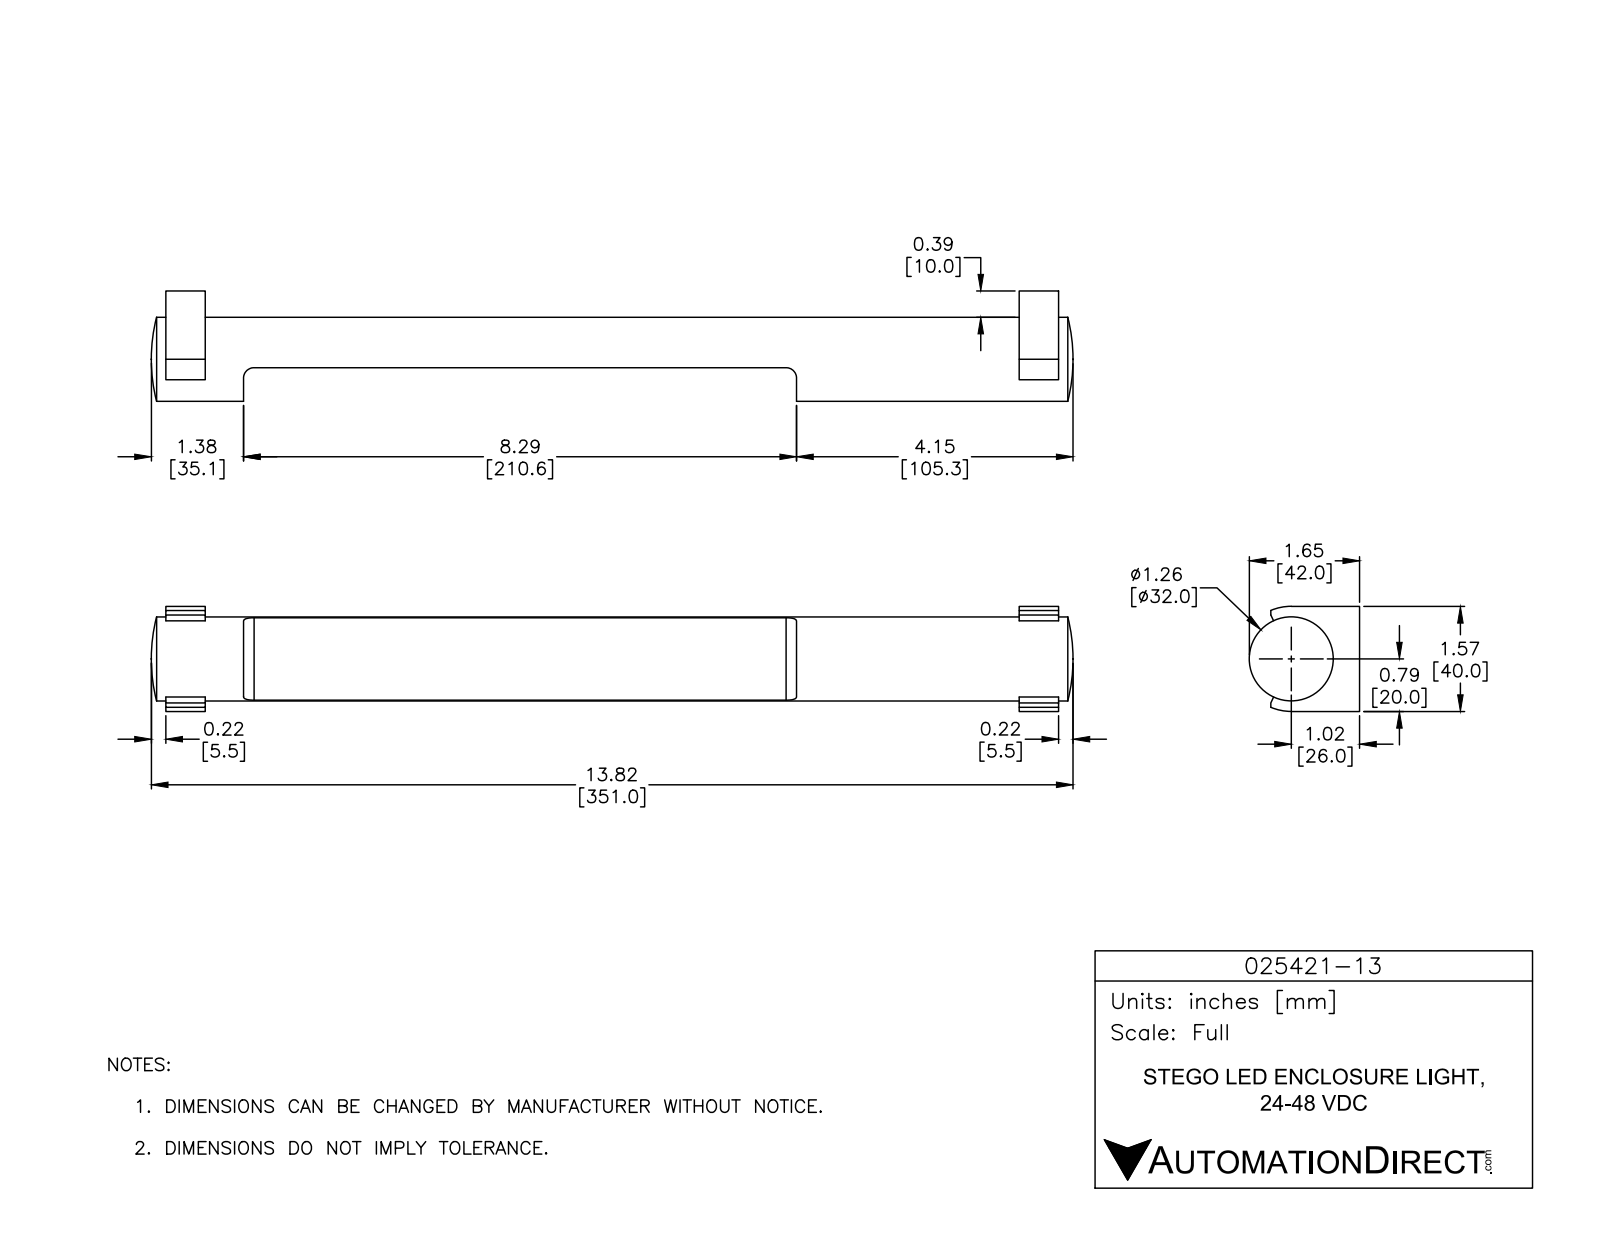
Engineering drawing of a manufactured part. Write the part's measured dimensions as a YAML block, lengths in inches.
part_name: "PRODUCT_NAME_1"
step_written_by: "ACIS (CONFIG_CONTROL_DESIGN)"
units: inches
bodies: {solids: 1, faces: 67, planar: 39, cylindrical: 24, other: 4}
overall_size: [13.819, 1.654, 1.575]
volume: 14.3
surface_area: 63.51
round_bosses_or_shafts:
  - {diameter: 1.26, count: 1}
partial_cylinders:
  - {radius: 0.122, count: 4}
  - {radius: 0.148, count: 2}
  - {radius: 0.157, count: 2}
  - {radius: 0.787, count: 1}
face_to_face_distances: [12.795, 0.591, 1.15, 1.575, 13.386, 12.205, 0.098, 0.492, 0.295, 1.28]
